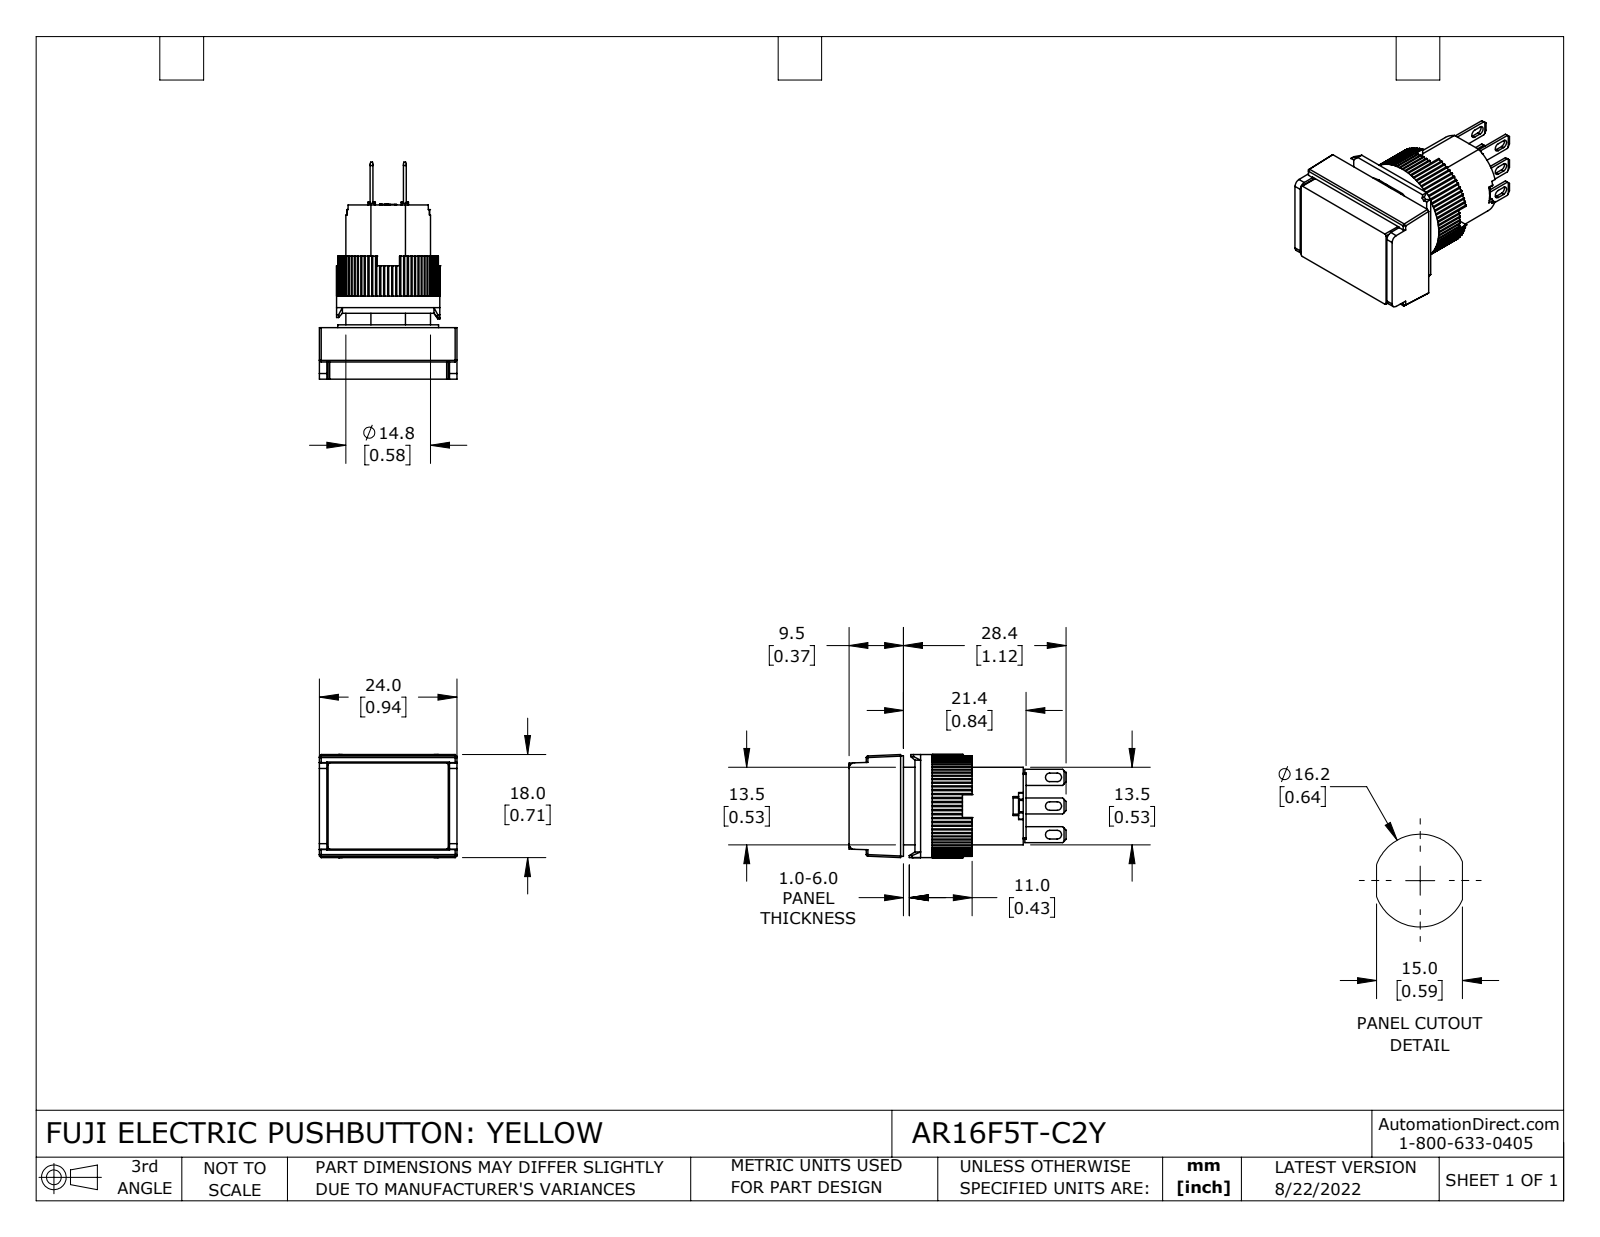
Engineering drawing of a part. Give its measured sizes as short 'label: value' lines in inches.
name: AR16F5T-C2Y
written by: SolidWorks 2021 (CONFIG_CONTROL_DESIGN)
unit: in
bodies: 12 solids, 813 faces (632 planar, 177 cylindrical, 4 other)
size: 1.492 × 0.945 × 0.709
volume: 0.443 in³; area: 9.124 in²
holes: 1× ⌀0.543, 1× ⌀0.583
bosses: 1× ⌀0.709, 1× ⌀0.693
rounds: 80× R0.01, 12× R0.008, 6× R0.012, 6× R0.03, 2× R0.039
face distances: 0.213, 0.354, 0.142, 0.492, 0.35, 0.138, 0.02, 0.843, 0.059, 0.453
